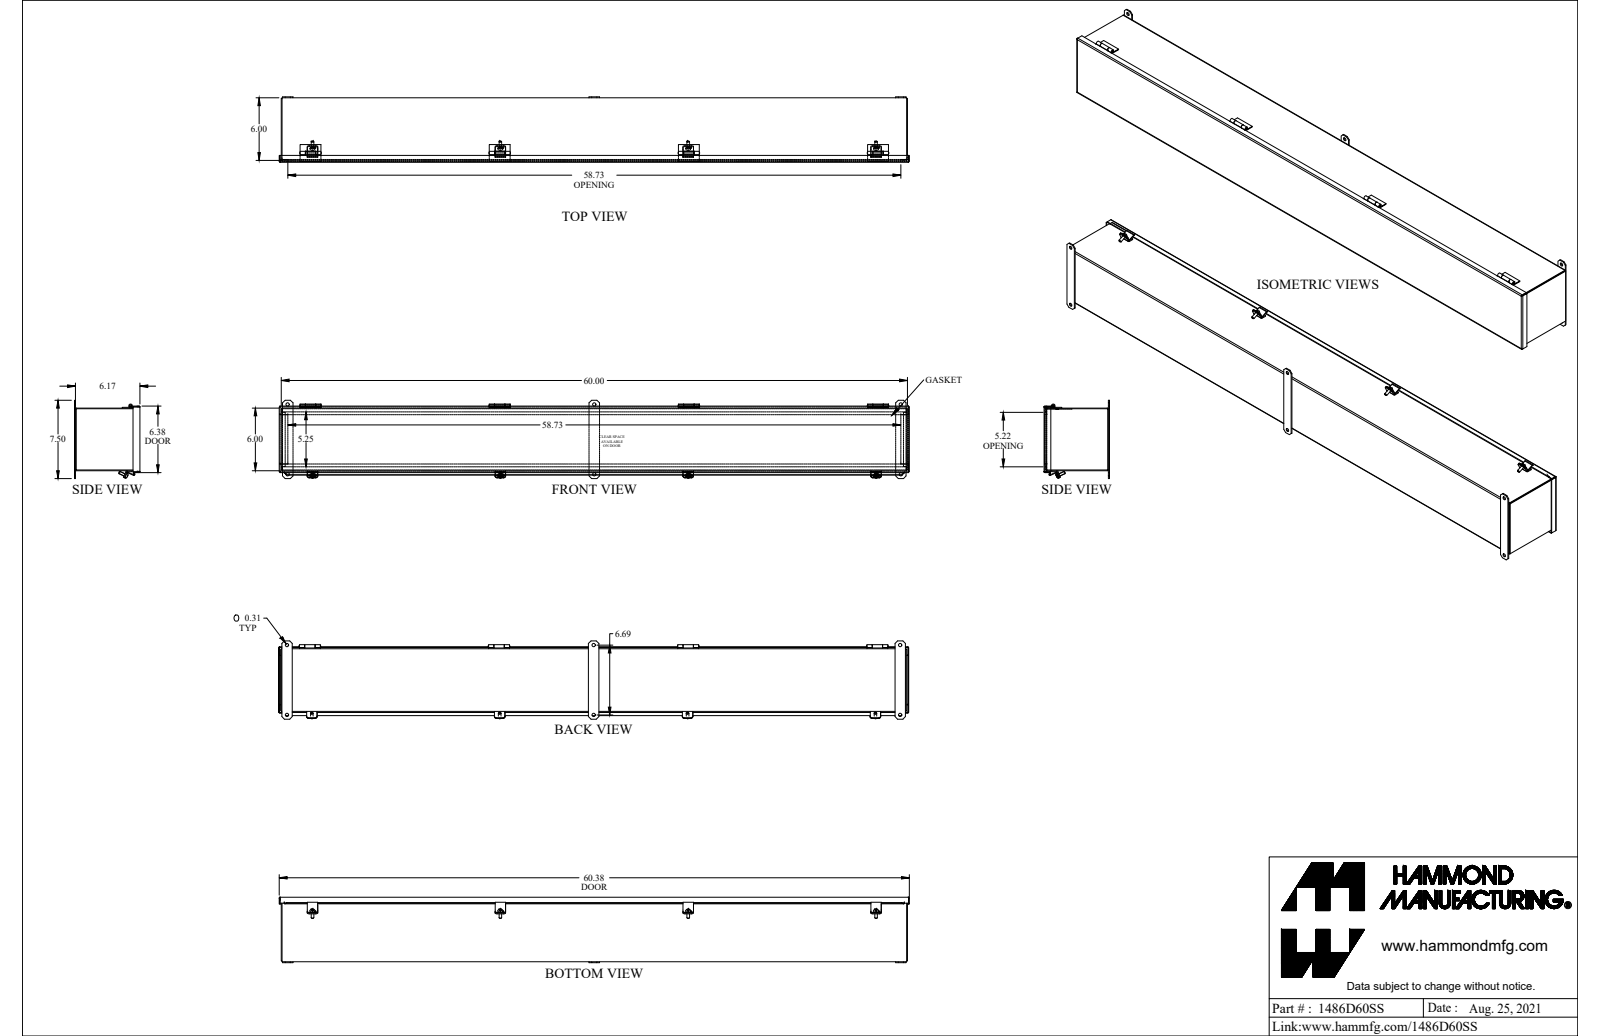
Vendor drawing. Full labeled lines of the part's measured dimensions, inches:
Part name (STEP PRODUCT): 1486D60SS
STEP written by: SolidWorks 2021 (AUTOMOTIVE_DESIGN)
Units: inches
Bodies: 13 solids, 632 faces (434 planar, 160 cylindrical, 38 other)
Overall size (bounding box): 60.375 × 7.5 × 6.267
Volume: 140.7 in³ · Surface area: 3 602 in²
Round holes (diameter × count): ⌀0.313 ×6, ⌀0.213 ×4, ⌀0.187 ×1
Round bosses / shafts (diameter × count): ⌀0.483 ×4, ⌀0.25 ×4, ⌀0.337 ×1, ⌀0.18 ×1
Partial cylindrical surfaces — rounded edges, fillets, slot ends (radius × count): R0.188 ×16, R0.036 ×11, R0.108 ×11, R0.01 ×8, R0.03 ×8, R0.141 ×8, R0.029 ×2, R0.086 ×2
Main face-to-face distances: 0.072, 5.928, 6.1, 5.856, 6, 6.028, 6.172, 0.187, 0.259, 5.913
Hole centre spacings: 30.127, 6.688, 18, 29.375, 36, 29.375, 54, 58.75
